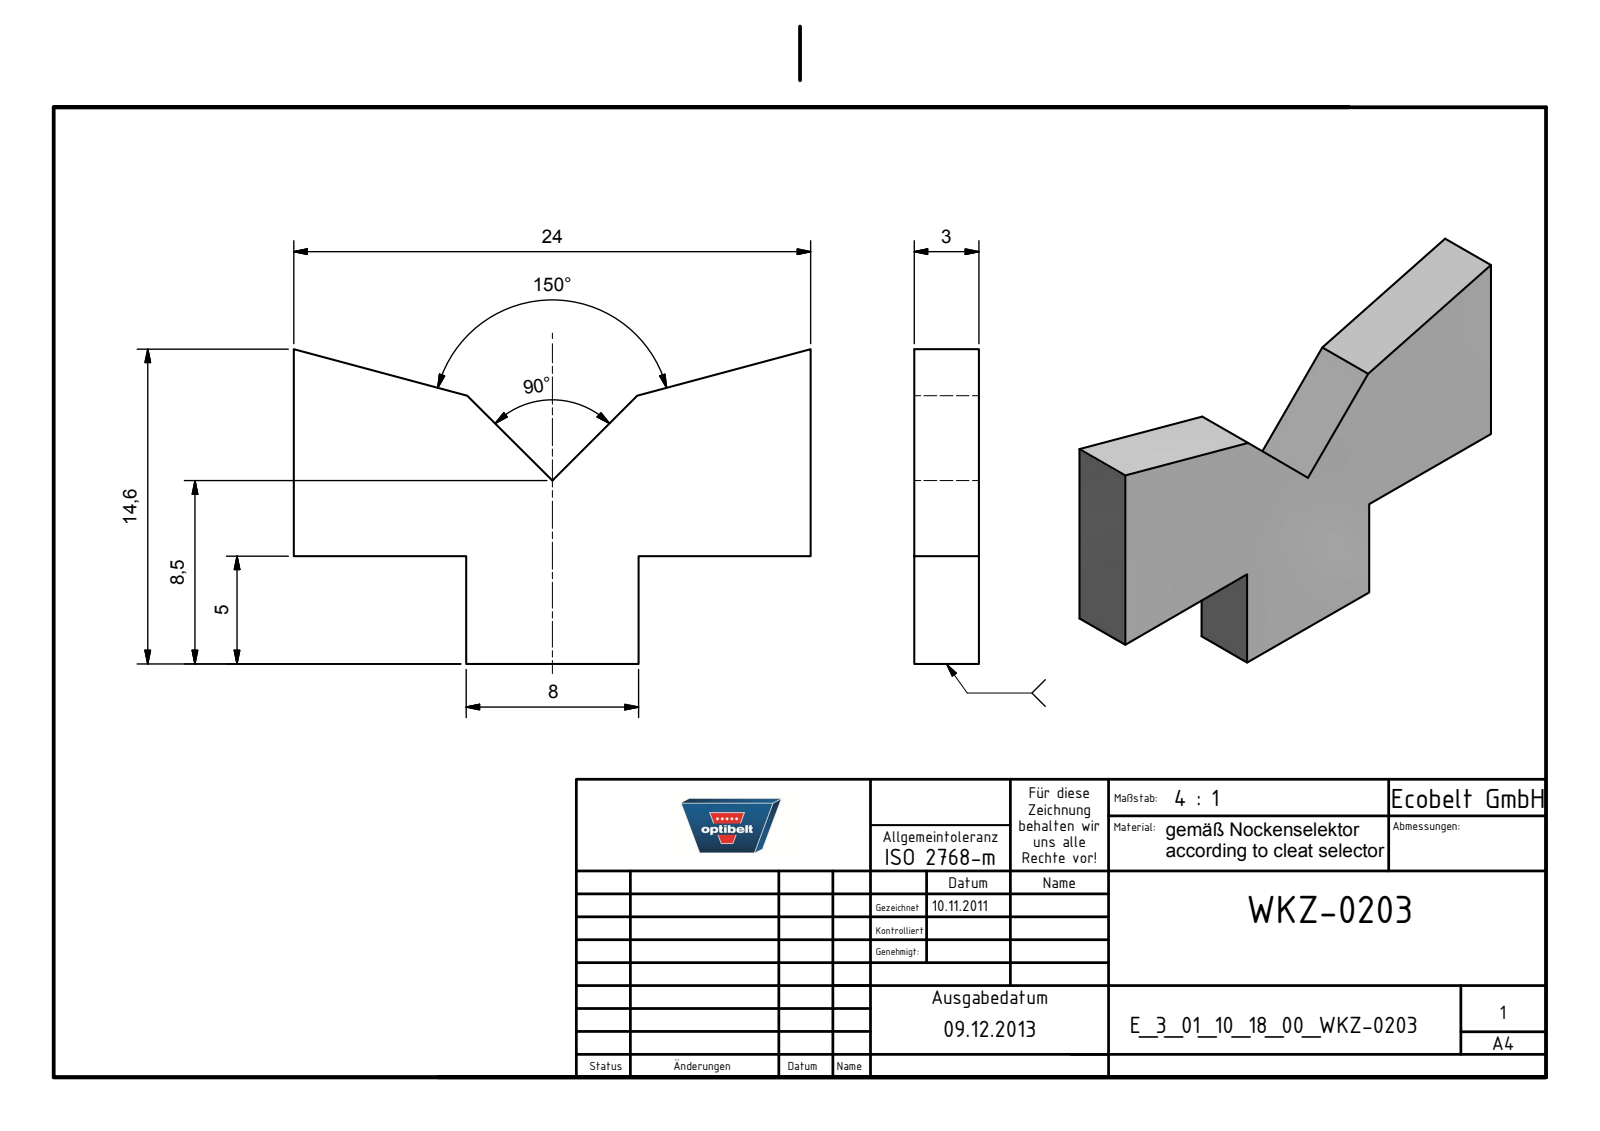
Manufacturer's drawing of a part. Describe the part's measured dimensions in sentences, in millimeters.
The part is named "E_3_01_10_18_00_WKZ-0203". Its 3-D file was written by "Autodesk Inventor 2025 (AUTOMOTIVE_DESIGN)". It is 1 solid with 13 faces: 13 planar, 0 cylindrical and 0 other. Overall it measures 24 by 14.6 by 3 millimeters. Its volume is 661 cubic millimeters and its surface area 684 square millimeters. The main face-to-face distances are 3, 8, 16, 24, 5.
